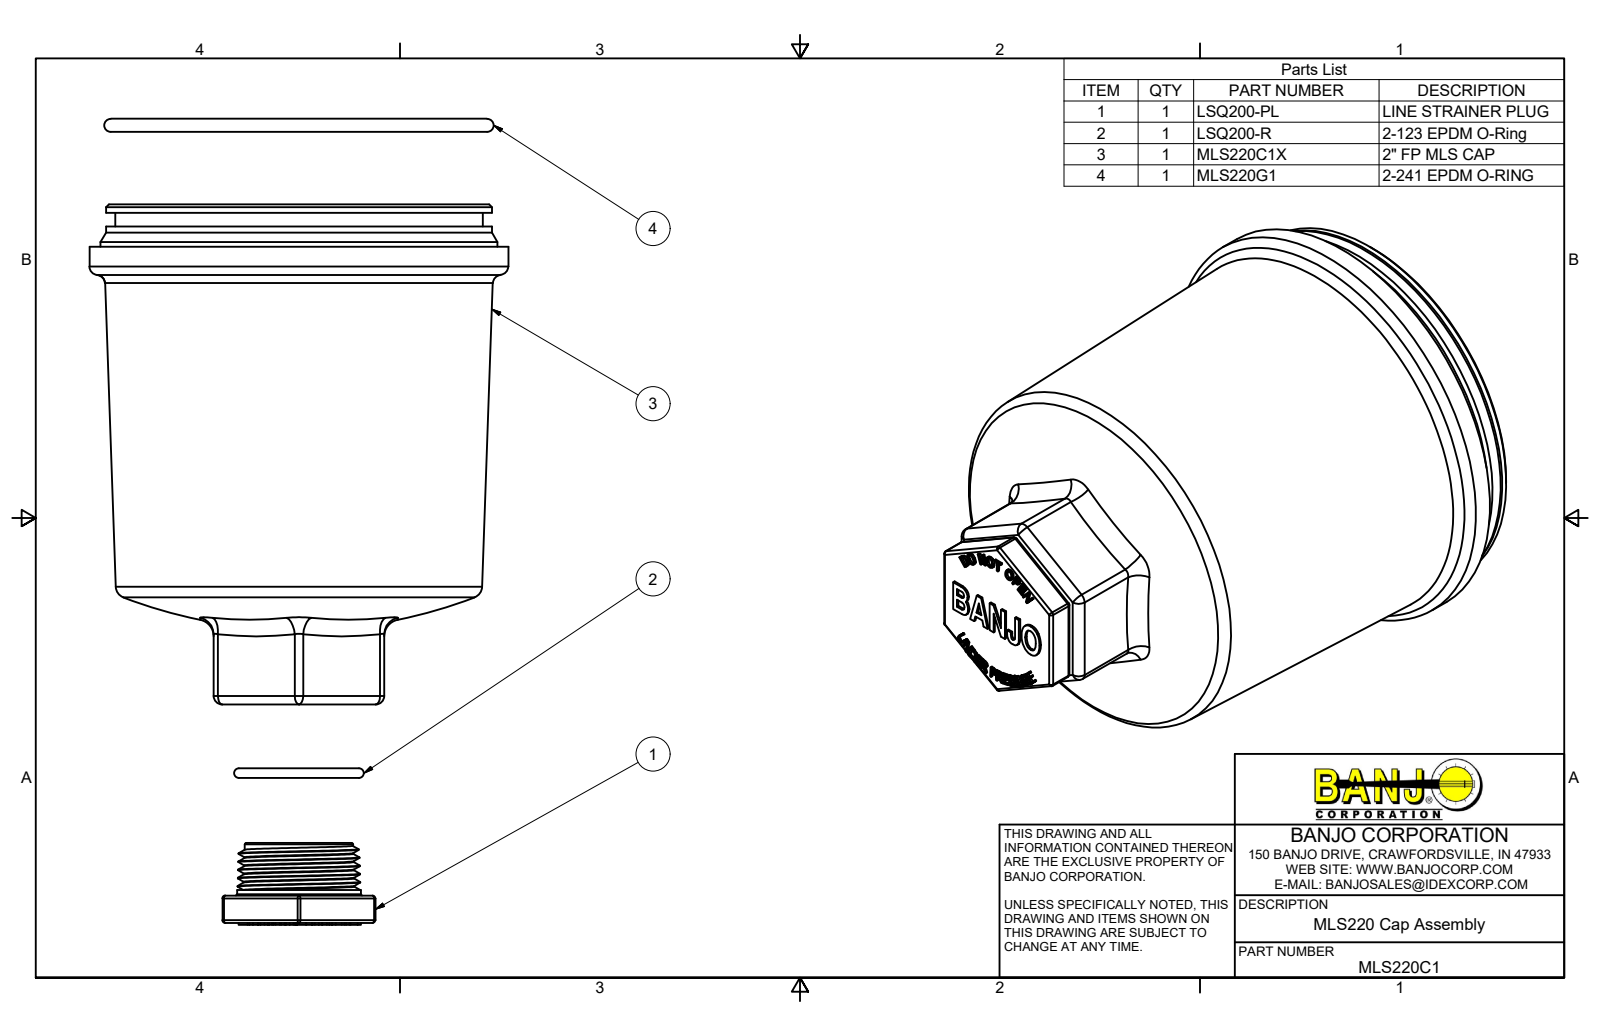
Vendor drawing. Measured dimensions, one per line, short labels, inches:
name: MLS220C1; MLS220C1X; LSQ200-PL; LSQ200-R (+1 more)
written by: Autodesk Inventor 2018 (AUTOMOTIVE_DESIGN)
unit: in
bodies: 4 solids, 570 faces (281 planar, 49 cylindrical, 240 other)
size: 5.65 × 4.45 × 4.45
volume: 20.32 in³; area: 152.7 in²
holes: 1× ⌀0.75, 1× ⌀1, 1× ⌀1.176, 1× ⌀3.53
bosses: 1× ⌀4.45, 1× ⌀4.215, 1× ⌀4.1, 1× ⌀3.905, 1× ⌀1.315
rounds: 18× R0.03, 12× R0.09
face distances: 1.812, 5.63, 5.18, 0.45, 0.093, 1.719, 5.394, 0.214, 0.236, 5.54
